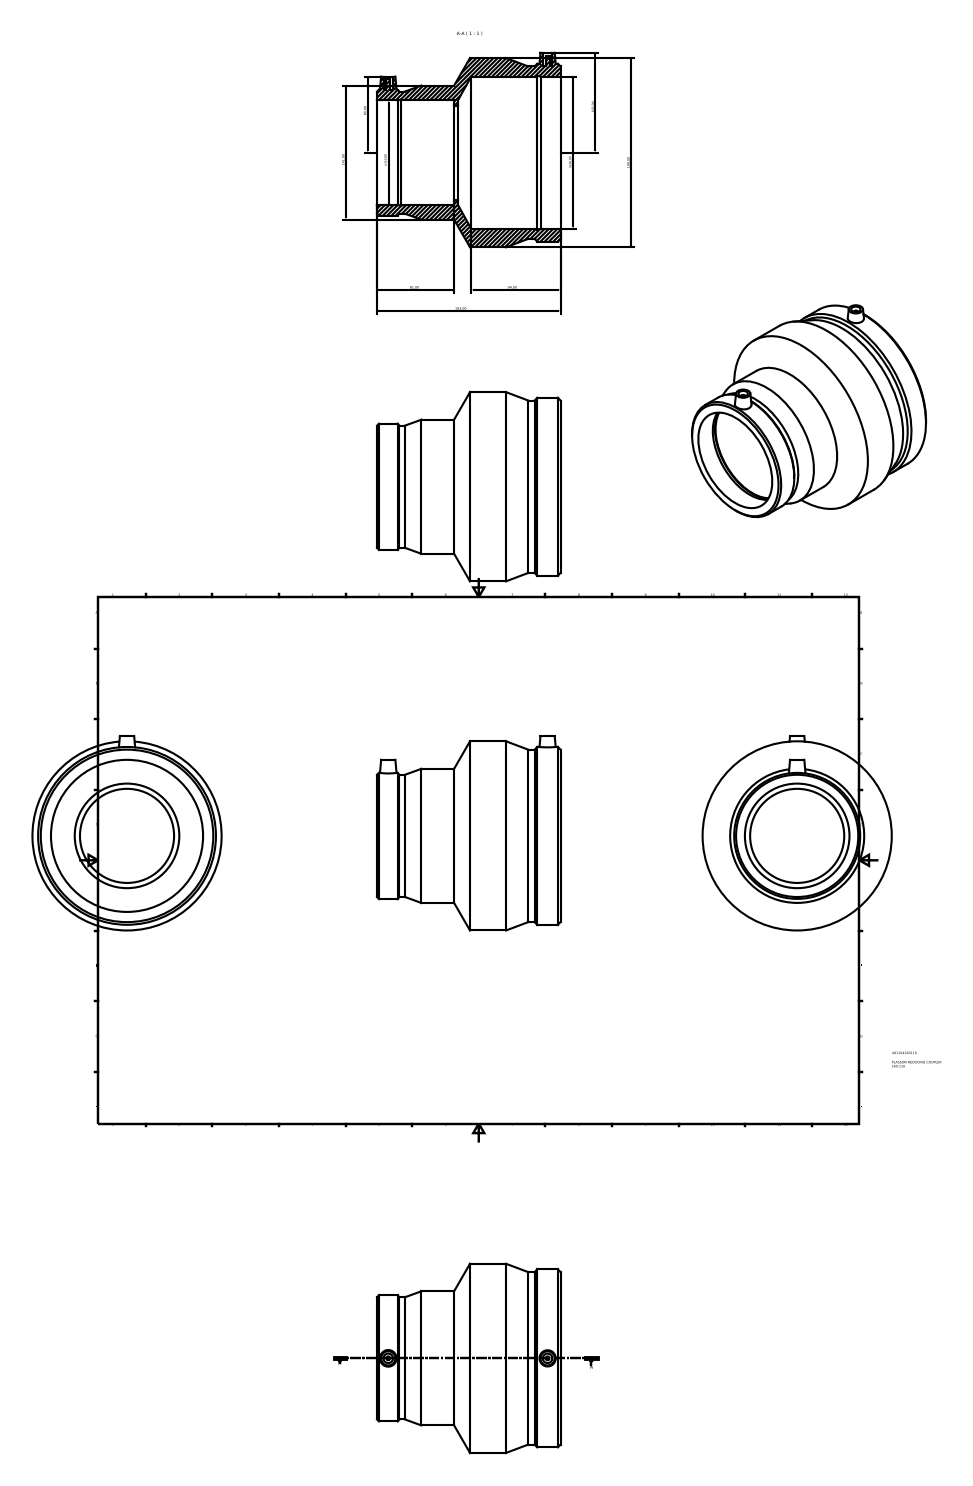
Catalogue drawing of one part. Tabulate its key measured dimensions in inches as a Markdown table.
| quantity | value |
| --- | --- |
| part name | 491104160110 |
| STEP written by | Autodesk Inventor 2015 (AUTOMOTIVE_DESIGN) |
| units | inches |
| bodies | 1 solid, 39 faces (12 planar, 15 cylindrical, 12 other) |
| overall size | 8.051 × 7.835 × 7.598 |
| volume | 87.69 in³ |
| surface area | 338.1 in² |
| round holes (diameter × count) | 0.394 × 2, 3.898 × 1, 4.331 × 1, 6.299 × 1 |
| round bosses / shafts (diameter × count) | 0.157 × 2, 7.835 × 1, 7.365 × 1, 7.144 × 1, 5.551 × 1, 5.218 × 1, 5.061 × 1 |
| main face-to-face distances | 7.598, 3.348, 4.25, 3.189, 0.159, 4.409, 6.636, 3.447, 3.287, 0.963 |
| hole center spacings | 6.599 |
